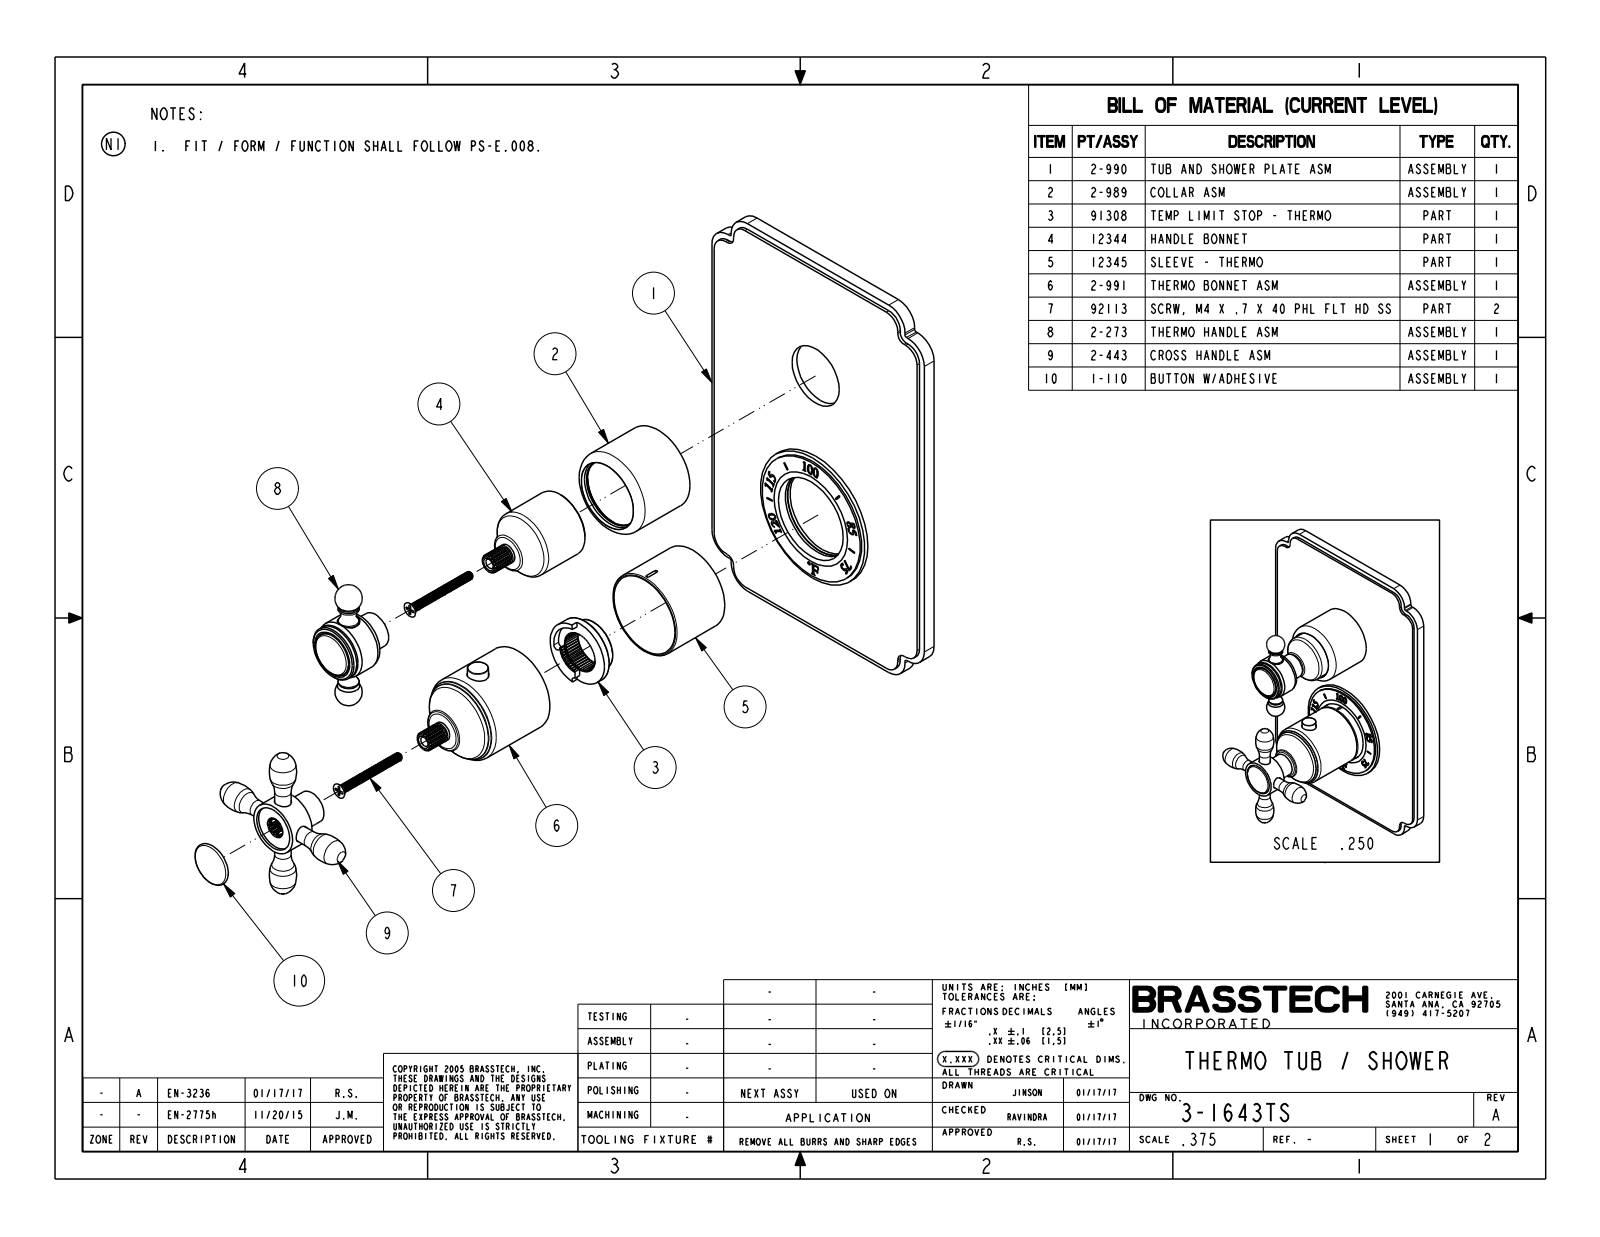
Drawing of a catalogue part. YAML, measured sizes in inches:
part_name: "12343_AF0; H-78_2_FEET_AF0; 91678; 2-990_AF0_ASM (+8 more)"
step_written_by: "PRO/ENGINEER BY PARAMETRIC TECHNOLOGY CORPORATION, 2013150 (CONFIG_CONTROL_DESIGN)"
units: inches
bodies: {solids: 30, faces: 2679, planar: 917, cylindrical: 694, other: 1068}
overall_size: [8.25, 5.5, 4.354]
volume: 10.55
surface_area: 347.2
round_holes:
  - {diameter: 0.136, count: 4}
  - {diameter: 0.19, count: 2}
  - {diameter: 0.206, count: 2}
  - {diameter: 0.27, count: 2}
  - {diameter: 0.313, count: 2}
  - {diameter: 0.063, count: 1}
  - {diameter: 0.079, count: 1}
  - {diameter: 0.1, count: 1}
  - {diameter: 0.126, count: 1}
  - {diameter: 0.205, count: 1}
  - {diameter: 0.276, count: 1}
  - {diameter: 0.276, count: 1}
round_bosses_or_shafts:
  - {diameter: 0.164, count: 4}
  - {diameter: 0.25, count: 3}
  - {diameter: 0.18, count: 3}
  - {diameter: 1.654, count: 2}
  - {diameter: 0.512, count: 2}
  - {diameter: 0.37, count: 2}
  - {diameter: 0.303, count: 2}
  - {diameter: 0.3, count: 2}
partial_cylinders:
  - {radius: 0.09, count: 8}
  - {radius: 0.295, count: 8}
  - {radius: 0.34, count: 8}
  - {radius: 0.42, count: 8}
  - {radius: 0.04, count: 4}
  - {radius: 0.12, count: 4}
  - {radius: 0.165, count: 4}
  - {radius: 0.37, count: 4}
face_to_face_distances: [0.08, 0.123, 0.043, 0.06, 0.063, 0.017, 0.25, 5.42, 0.233, 0.19]
hole_center_spacings: [0.423, 0.554, 1.293, 1.716, 2.596, 3.15]
